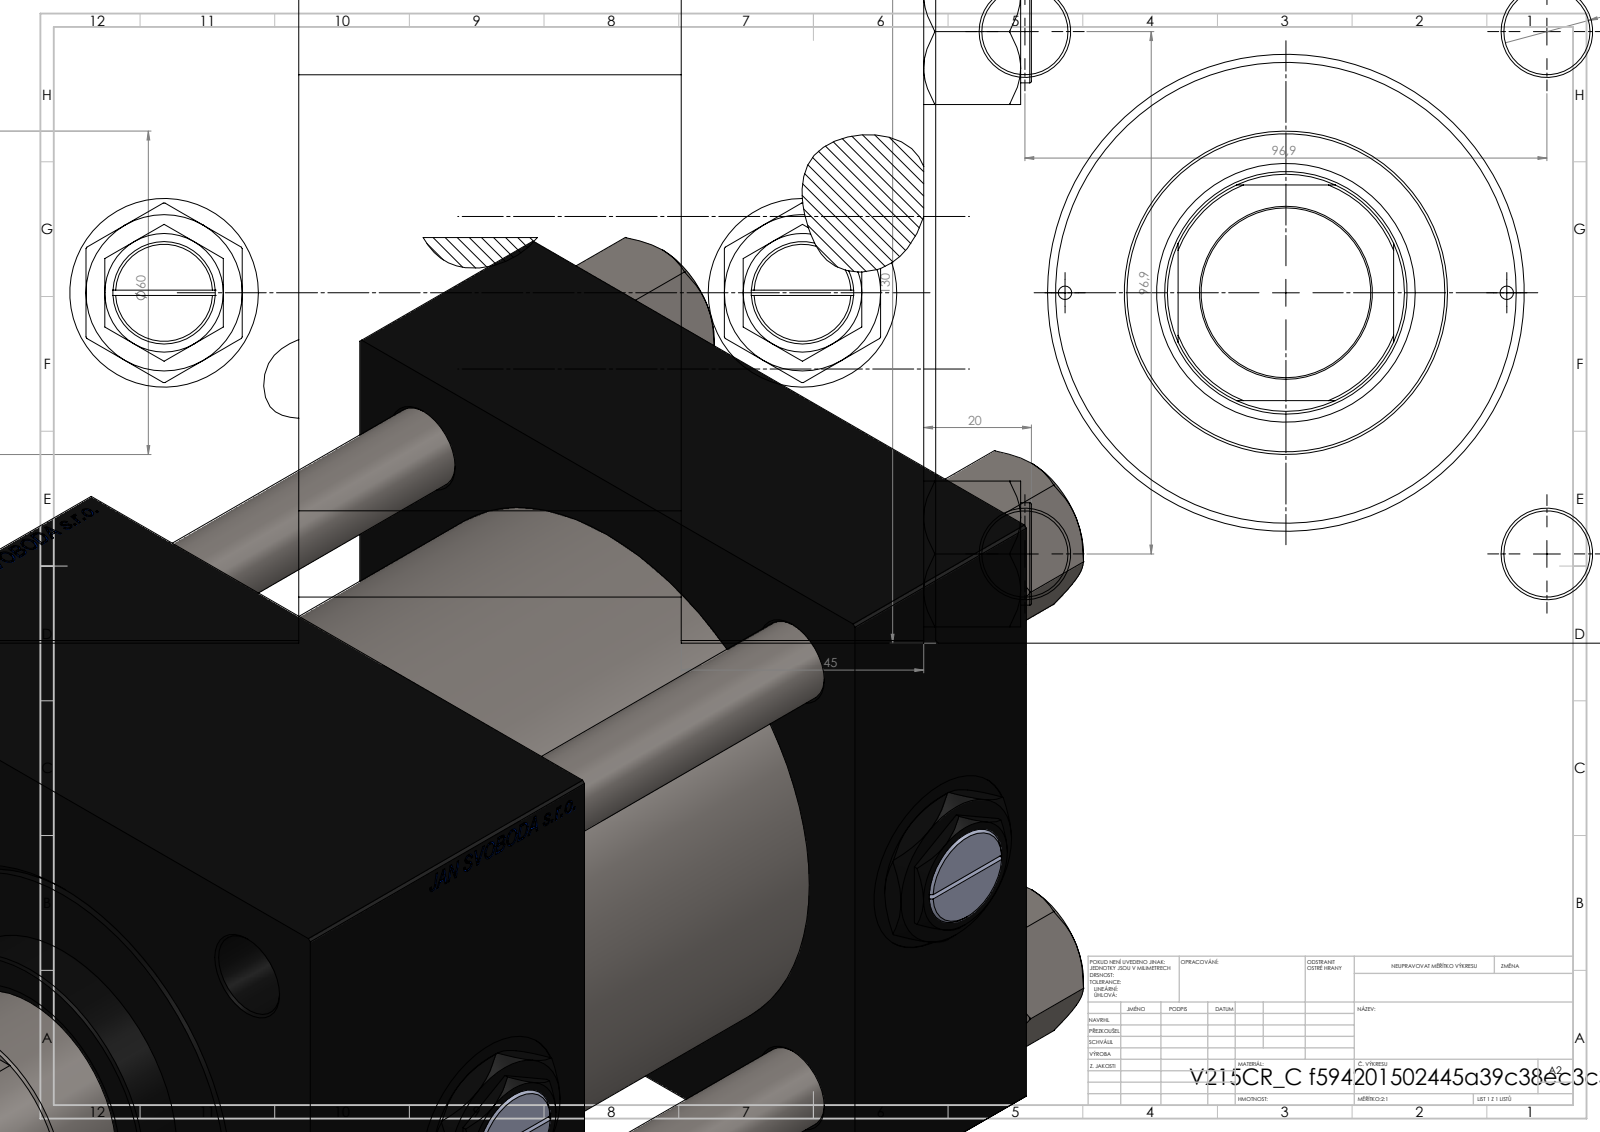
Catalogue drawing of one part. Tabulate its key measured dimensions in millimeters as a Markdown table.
| quantity | value |
| --- | --- |
| part name | V215_VC_A; Zatka_pro_OIL_PORT; V215CR_VCP_C; V215CR_C_Body (+2 more) |
| STEP written by | SolidWorks 2019 (CONFIG_CONTROL_DESIGN) |
| units | millimeters |
| bodies | 13 solids, 1303 faces (623 planar, 102 cylindrical, 578 other) |
| overall size | 243 × 137 × 130 |
| volume | 2 411 000 mm³ |
| surface area | 333 527 mm² |
| round holes (diameter × count) | 16 × 4, 2.5 × 2, 7 × 2, 26.44 × 2, 35 × 2, 31.5 × 1, 45 × 1, 48 × 1, 76 × 1, 85.5 × 1, 100 × 1 |
| round bosses / shafts (diameter × count) | 19 × 4, 106 × 1, 60 × 1 |
| partial cylindrical surfaces (radius × count) | 22 × 1 |
| main face-to-face distances | 130, 45, 188, 143, 116, 71, 72, 20, 92, 96 |
| hole center spacings | 49.02, 68.52, 96.9, 101.73, 41, 137.04, 82, 118.5 |
